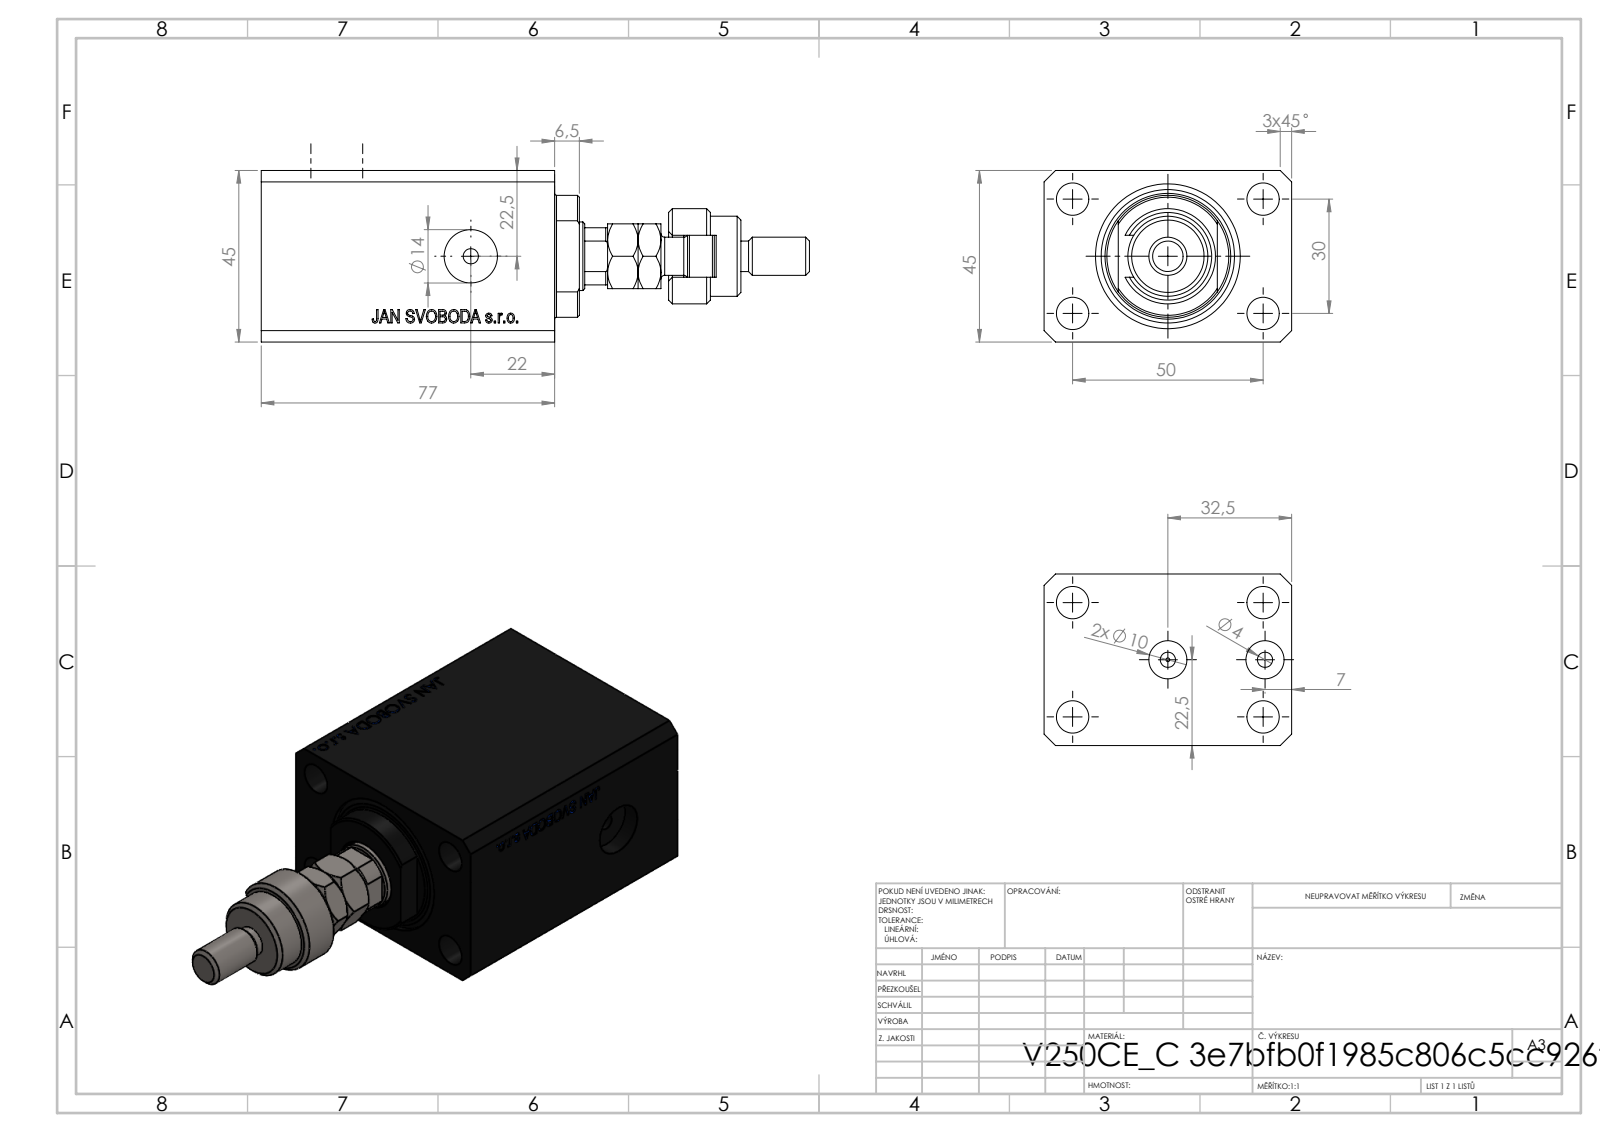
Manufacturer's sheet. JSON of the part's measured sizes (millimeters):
{"part_name": "V250CE_VC_C; V250CE_C_Body; MFA; V250CE_C_VCP (+1 more)", "step_written_by": "SolidWorks 2019 (CONFIG_CONTROL_DESIGN)", "units": "millimeters", "bodies": {"solids": 5, "faces": 957, "planar": 456, "cylindrical": 63, "other": 438}, "overall_size": [144, 65, 45], "volume_mm3": 215235, "surface_area_mm2": 56199, "round_holes": [[8.5, 5], [4, 4], [14, 2], [1.25, 1], [10, 1], [18, 1], [38, 1]], "round_bosses_or_shafts": [[25, 1], [21, 1], [16, 1], [10, 1], [8, 1]], "partial_cylinders_radius": [[5.5, 1], [8.5, 1], [8.75, 1], [16, 1]], "face_to_face_distances": [45, 65, 14, 63, 77, 6.9, 56.1, 70.1, 28, 6.5], "hole_center_spacings": [29.15, 15.01, 30, 50, 52.68, 58.31, 25.5, 33]}
